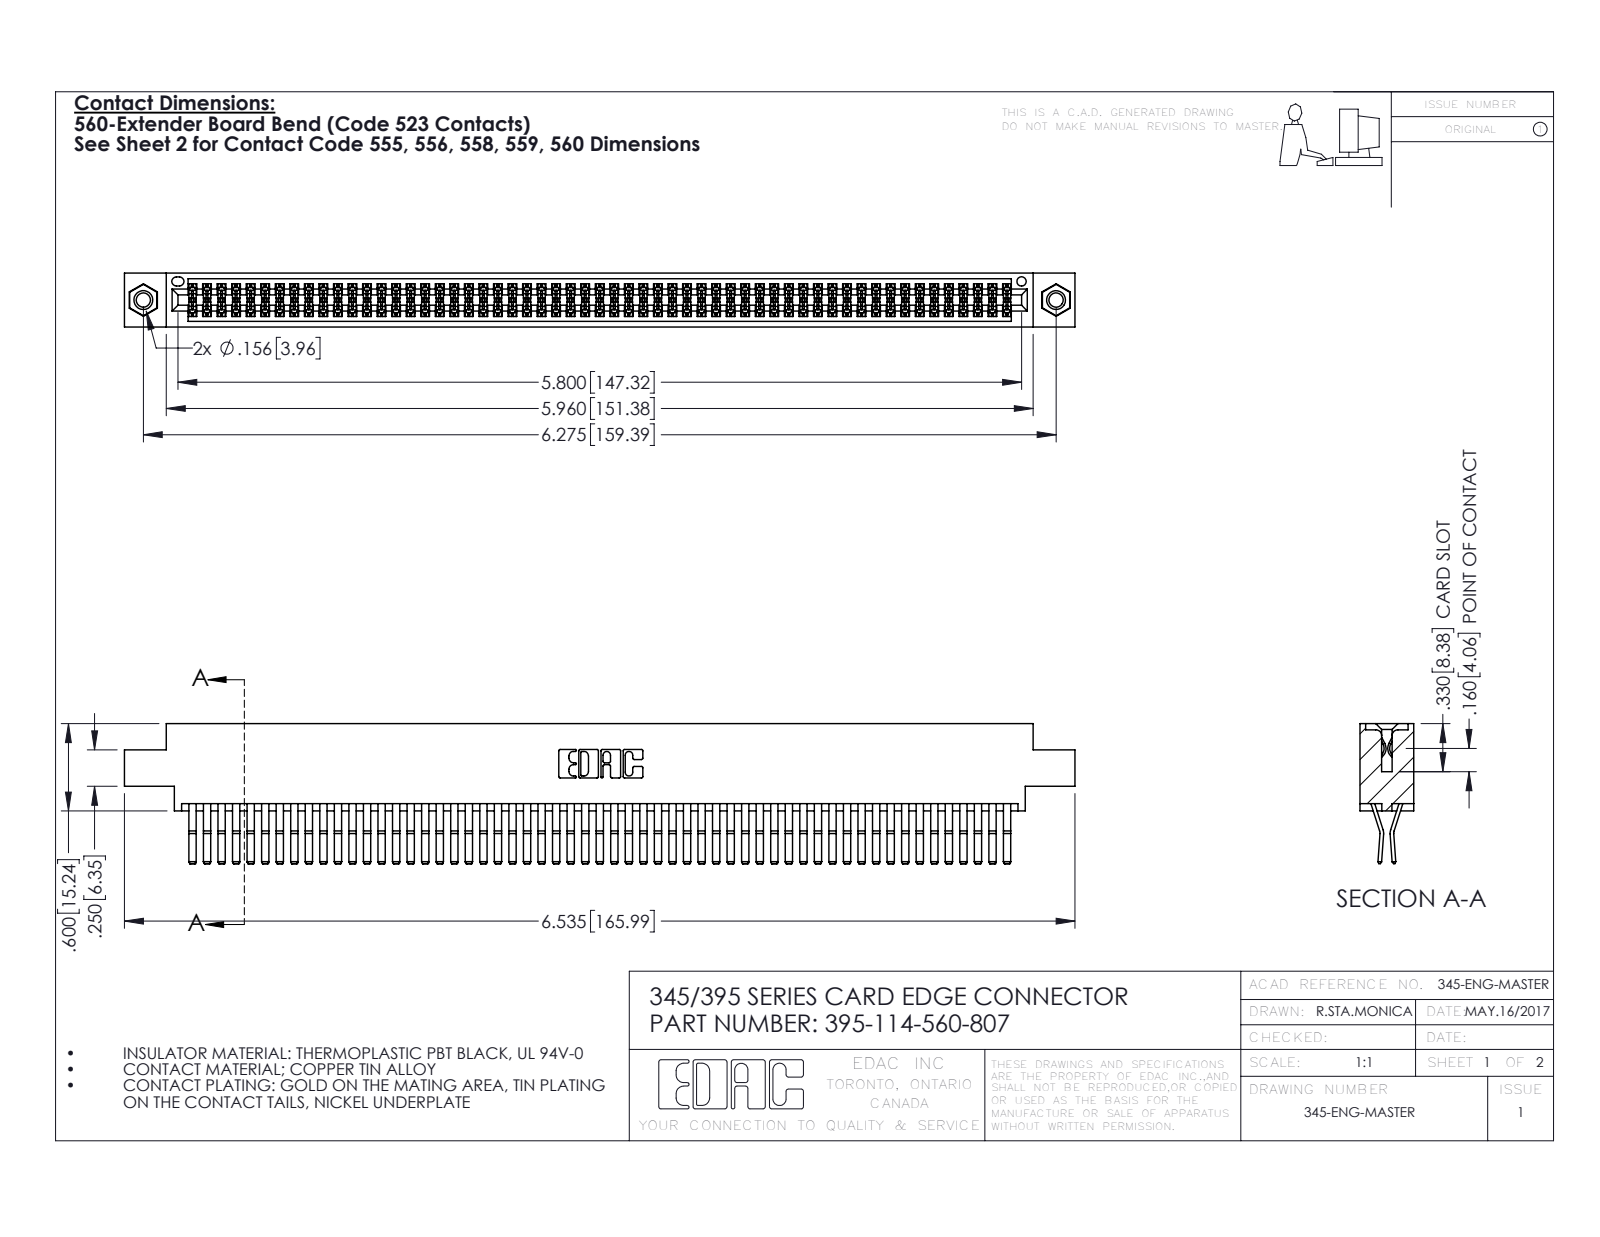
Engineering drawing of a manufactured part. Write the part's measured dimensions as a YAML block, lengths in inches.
part_name: "345 Part_0.170 Offset - 0.156 Dia-TI; 345-292-001_560 Tail; 345-250-001_345-250-005-103; 395-114-560-807"
step_written_by: "SolidWorks 2016 (CONFIG_CONTROL_DESIGN)"
units: inches
bodies: {solids: 117, faces: 6118, planar: 3878, cylindrical: 2224, other: 16}
overall_size: [6.535, 0.962, 0.37]
volume: 1.03
surface_area: 42.38
round_holes:
  - {diameter: 0.098, count: 2}
  - {diameter: 0.125, count: 2}
  - {diameter: 0.156, count: 2}
  - {diameter: 0.064, count: 1}
round_bosses_or_shafts:
  - {diameter: 0.155, count: 2}
partial_cylinders:
  - {radius: 0.006, count: 172}
  - {radius: 0.01, count: 22}
  - {radius: 0.007, count: 6}
  - {radius: 0.031, count: 6}
  - {radius: 0.026, count: 3}
  - {radius: 0.01, count: 2}
  - {radius: 0.014, count: 2}
  - {radius: 0.019, count: 2}
face_to_face_distances: [0.025, 0.072, 0.298, 0.37, 0.2, 0.098, 0.272, 0.225, 0.175, 0.149]
hole_center_spacings: [0.27, 6.039, 6.275]
